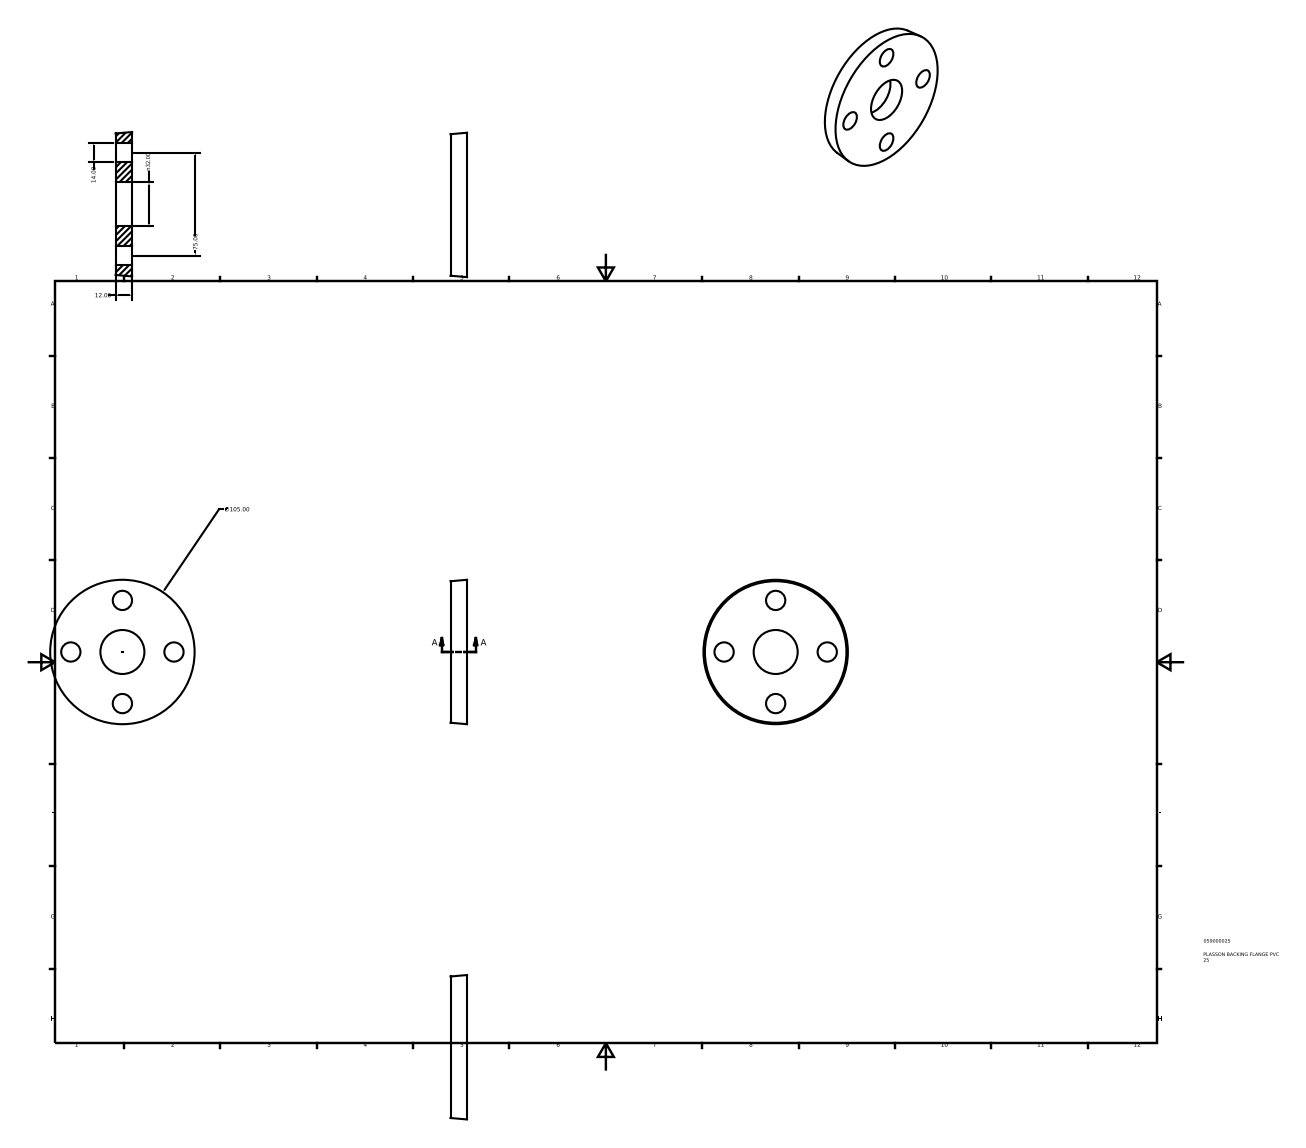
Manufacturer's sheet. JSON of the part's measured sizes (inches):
{"part_name": "059000025", "step_written_by": "Autodesk Inventor 2015 (AUTOMOTIVE_DESIGN)", "units": "inches", "bodies": {"solids": 1, "faces": 8, "planar": 2, "cylindrical": 5, "other": 1}, "overall_size": [4.134, 4.134, 0.472], "volume_in3": 5.175, "surface_area_in2": 33.15, "round_holes": [[0.551, 4], [1.26, 1]], "face_to_face_distances": [0.472], "hole_center_spacings": [1.476, 2.088, 2.953]}
